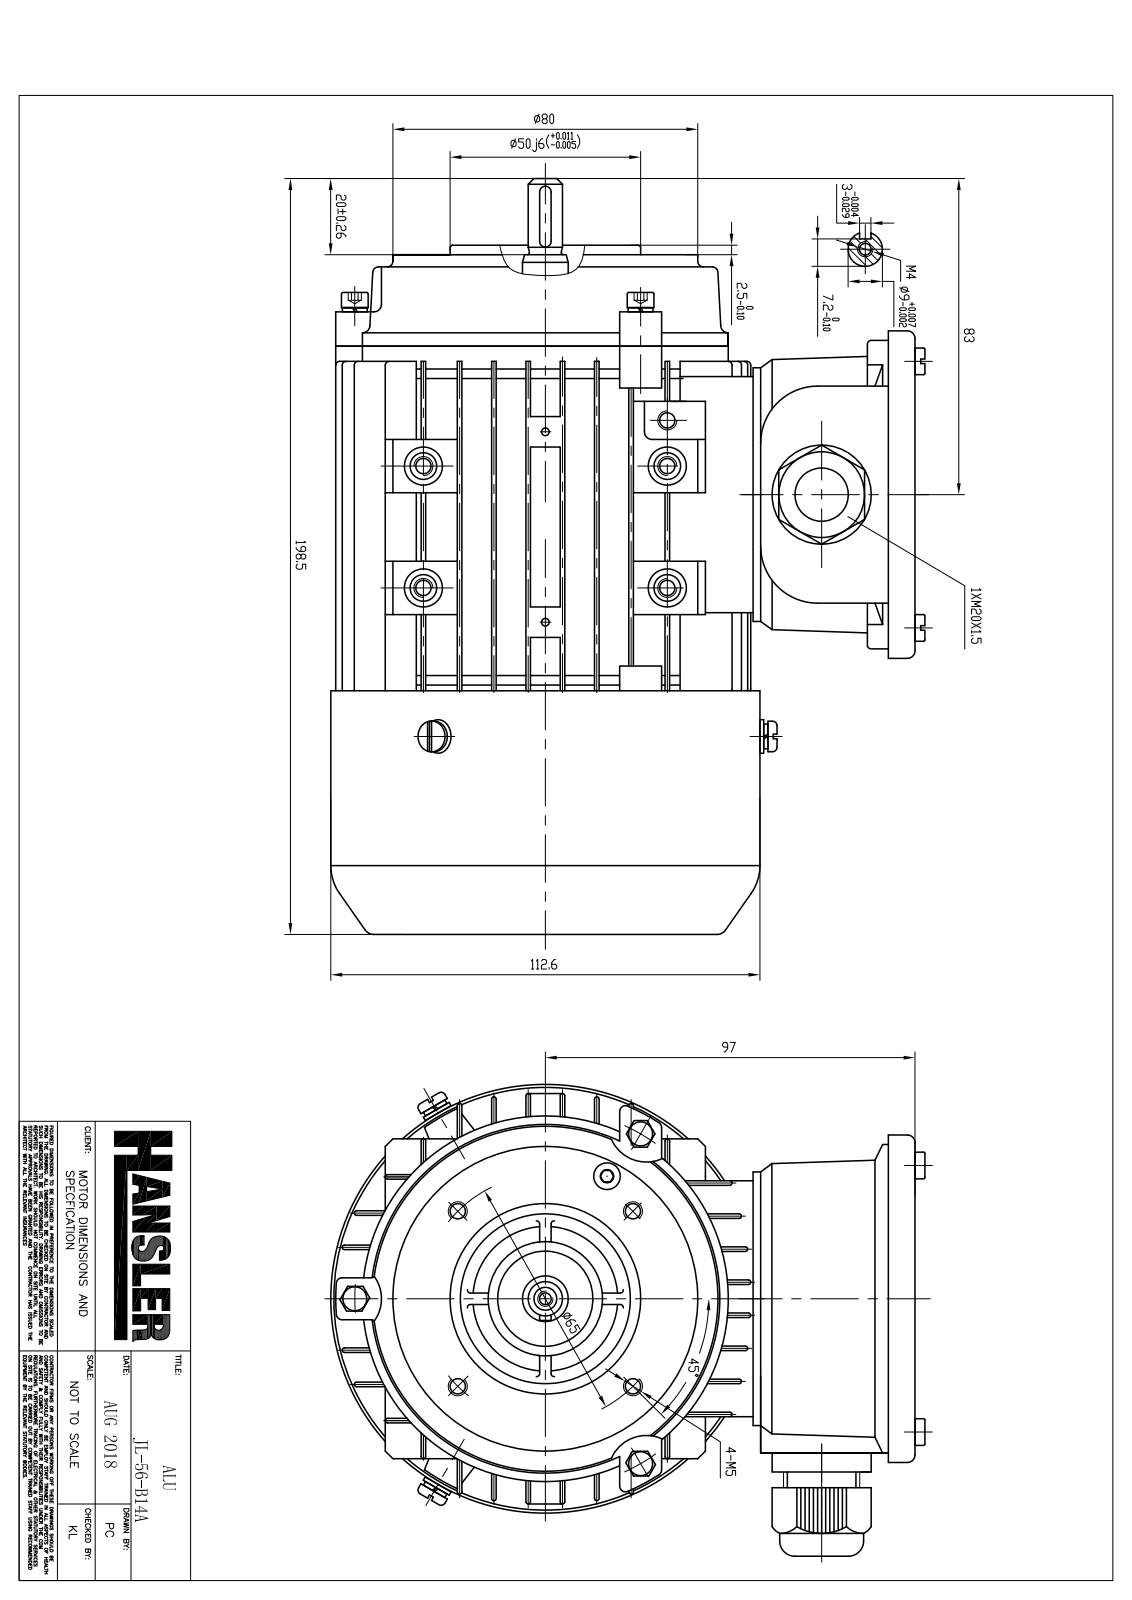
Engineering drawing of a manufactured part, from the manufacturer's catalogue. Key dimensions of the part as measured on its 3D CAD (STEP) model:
Part name (STEP PRODUCT): JL-56-B14A
STEP written by: SIEMENS PLM Software NX 12.0 (AP203_CONFIGURATION_CONTROLLED_3D_DESIGN_OF_MECHANICAL_PARTS_AND_ASSEMBLIES_MIM_LF)
Units: millimetres
Bodies: 37 solids, 3028 faces (1630 planar, 968 cylindrical, 430 other)
Overall size (bounding box): 198.42 × 154.7 × 119.88
Volume: 380 407 mm³ · Surface area: 317 593 mm²
Round holes (diameter × count): ⌀4 ×17, ⌀3 ×14, ⌀10 ×8, ⌀4.7 ×7, ⌀4.25 ×6, ⌀5 ×4, ⌀2 ×3, ⌀4.9 ×3, ⌀12 ×3, ⌀4.13 ×1, ⌀8 ×1, ⌀10.4 ×1
Round bosses / shafts (diameter × count): ⌀3.55 ×10, ⌀7 ×8, ⌀6.45 ×6, ⌀4 ×6, ⌀10 ×4, ⌀11 ×2, ⌀112.6 ×1, ⌀96 ×1
Partial cylindrical surfaces — rounded edges, fillets, slot ends (radius × count): R0.5 ×280, R3 ×36, R5 ×20, R2 ×19, R1 ×13, R1.5 ×12, R2.5 ×6, R5.5 ×4
Main face-to-face distances: 8.68, 17.36, 26.04, 2, 1.2, 9.88, 34.72, 7.48, 18.56, 4
Hole centre spacings: 44, 58.46, 32, 50, 12, 17.63, 18.38, 25.81
